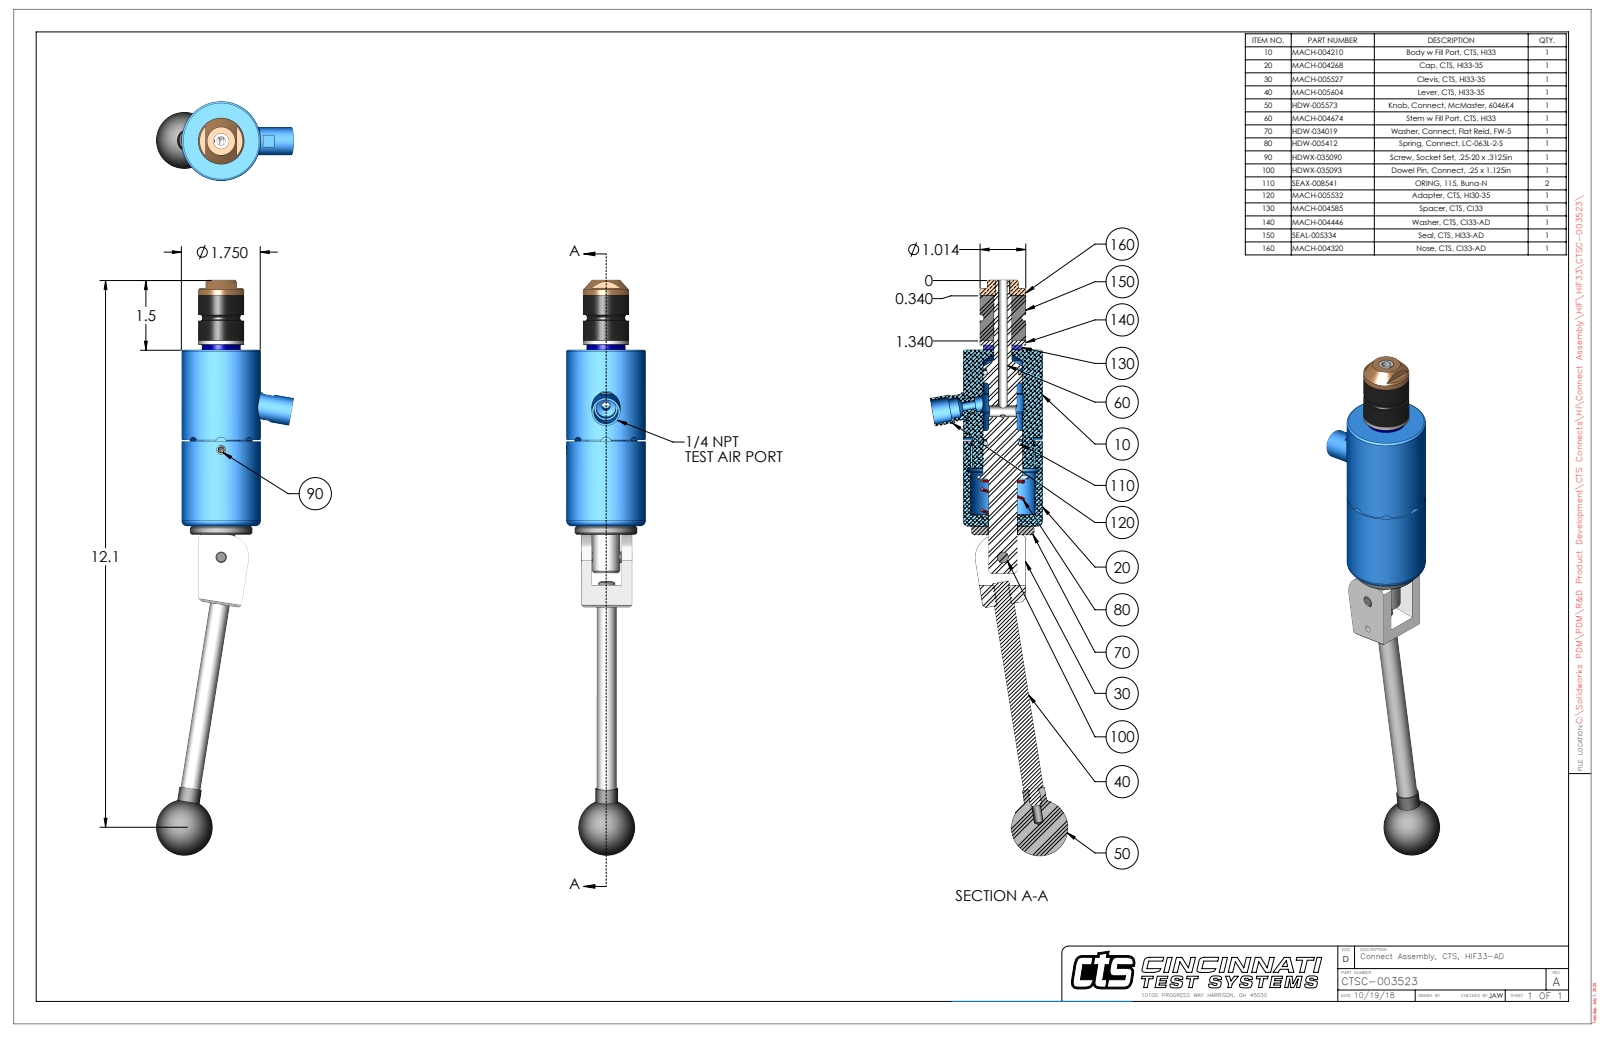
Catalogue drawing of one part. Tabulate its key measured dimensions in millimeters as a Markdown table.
| quantity | value |
| --- | --- |
| part name | CTSC-003523 |
| STEP written by | SolidWorks 2023 (AUTOMOTIVE_DESIGN) |
| units | millimeters |
| bodies | 10 solids, 296 faces (106 planar, 124 cylindrical, 66 other) |
| overall size | 323.9 × 77.3 × 44.5 |
| volume | 224 300 mm³ |
| surface area | 49 100 mm² |
| round holes (diameter × count) | 5.1 × 2, 8 × 2, 3.8 × 1, 4.7 × 1, 5.2 × 1, 6.3 × 1, 6.4 × 1, 6.4 × 1, 9.9 × 1, 10.1 × 1, 10.2 × 1, 11.1 × 1 |
| round bosses / shafts (diameter × count) | 9.5 × 2, 7.9 × 2, 6.4 × 2, 44.5 × 1, 35.1 × 1, 25.8 × 1, 21.8 × 1, 15.9 × 1 |
| partial cylindrical surfaces (radius × count) | 3.2 × 4, 0.7 × 2, 3.6 × 1, 4.2 × 1, 8.4 × 1, 12.7 × 1, 17.7 × 1, 20.7 × 1 |
| main face-to-face distances | 99.2, 28.4, 30.7, 129.9, 25.4, 5.3, 104.5, 134.7, 109.3, 104 |
| hole center spacings | 18.8, 60.4, 79.1 |
